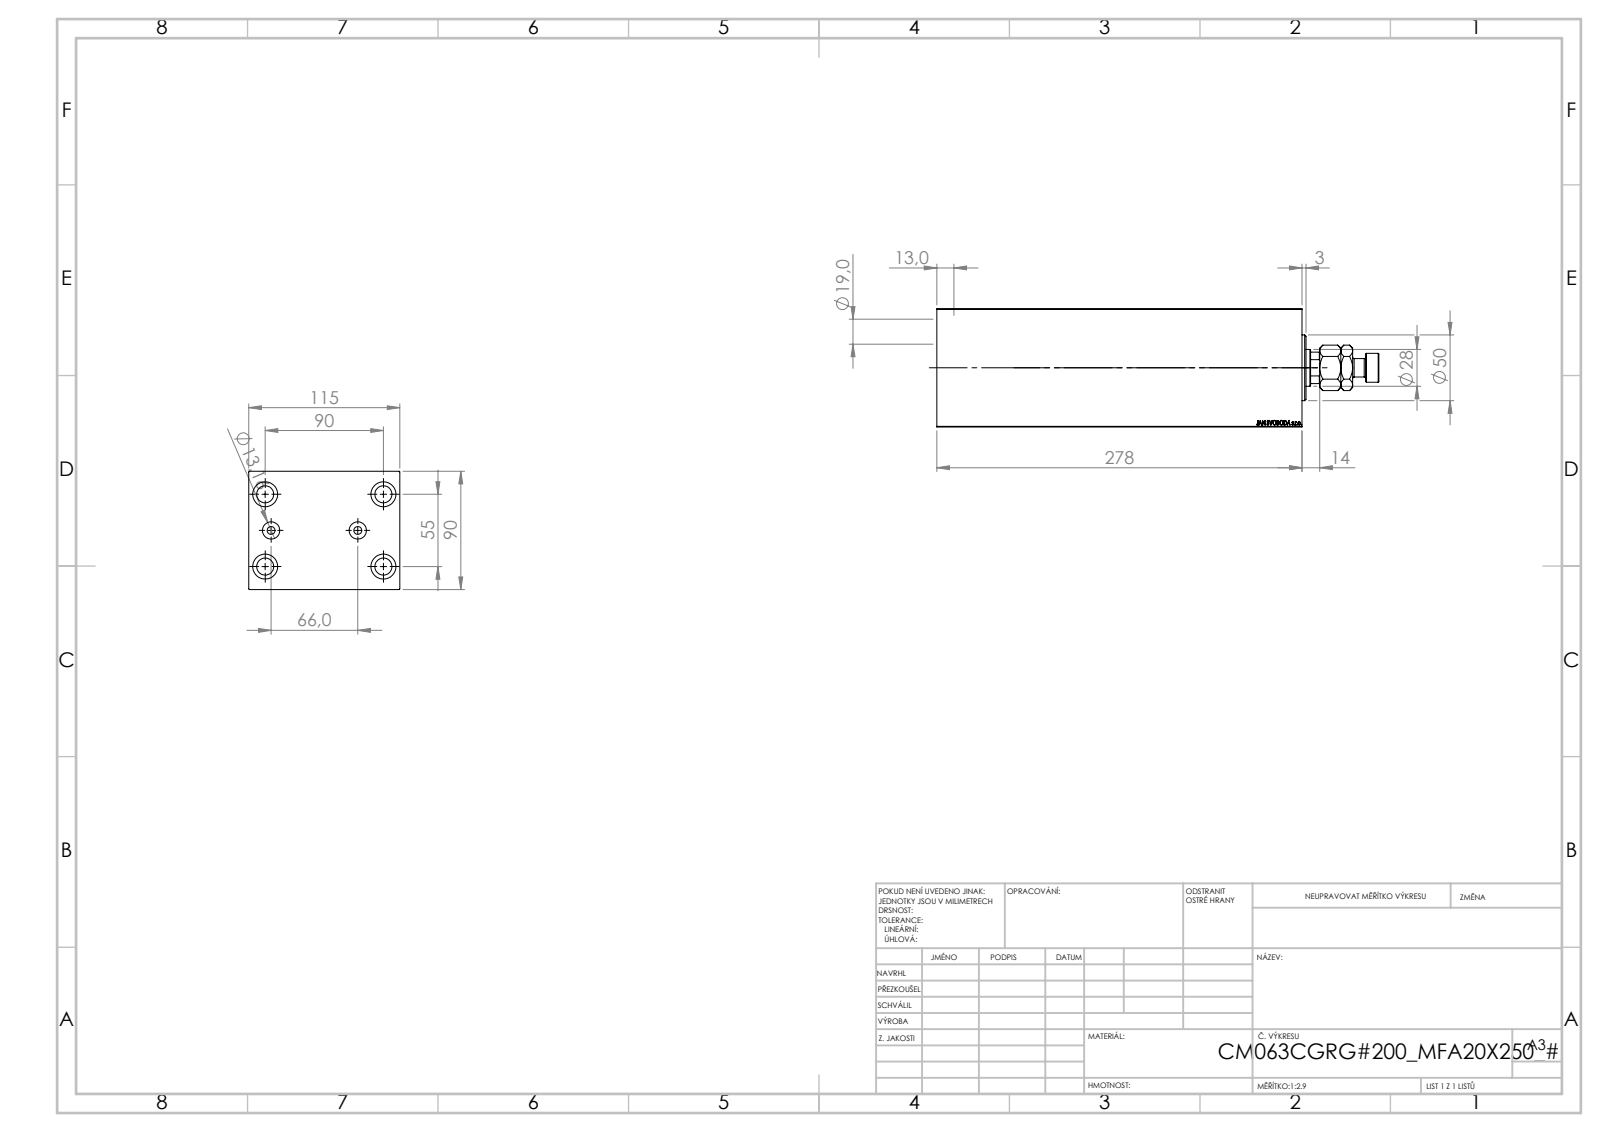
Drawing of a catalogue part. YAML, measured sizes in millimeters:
part_name: "V450CM_C_VCP; V450CM_VC_B; MFA; V450CM_C_Body"
step_written_by: "SolidWorks 2019 (CONFIG_CONTROL_DESIGN)"
units: millimeters
bodies: {solids: 4, faces: 913, planar: 425, cylindrical: 62, other: 426}
overall_size: [336.5, 115, 90]
volume: 2228000
surface_area: 294360
round_holes:
  - {diameter: 13, count: 4}
  - {diameter: 19, count: 4}
  - {diameter: 6, count: 2}
  - {diameter: 13.16, count: 2}
  - {diameter: 18.5, count: 1}
  - {diameter: 28, count: 1}
  - {diameter: 31.5, count: 1}
  - {diameter: 63, count: 1}
  - {diameter: 65, count: 1}
  - {diameter: 72, count: 1}
round_bosses_or_shafts:
  - {diameter: 50, count: 1}
  - {diameter: 22, count: 1}
  - {diameter: 14, count: 1}
partial_cylinders:
  - {radius: 13.5, count: 1}
face_to_face_distances: [90, 115, 278, 17.5, 260.5, 29.3, 231.2, 248.7, 229.3, 200]
hole_center_spacings: [30, 52.74, 82.71, 33, 55, 90, 105.48, 66]
